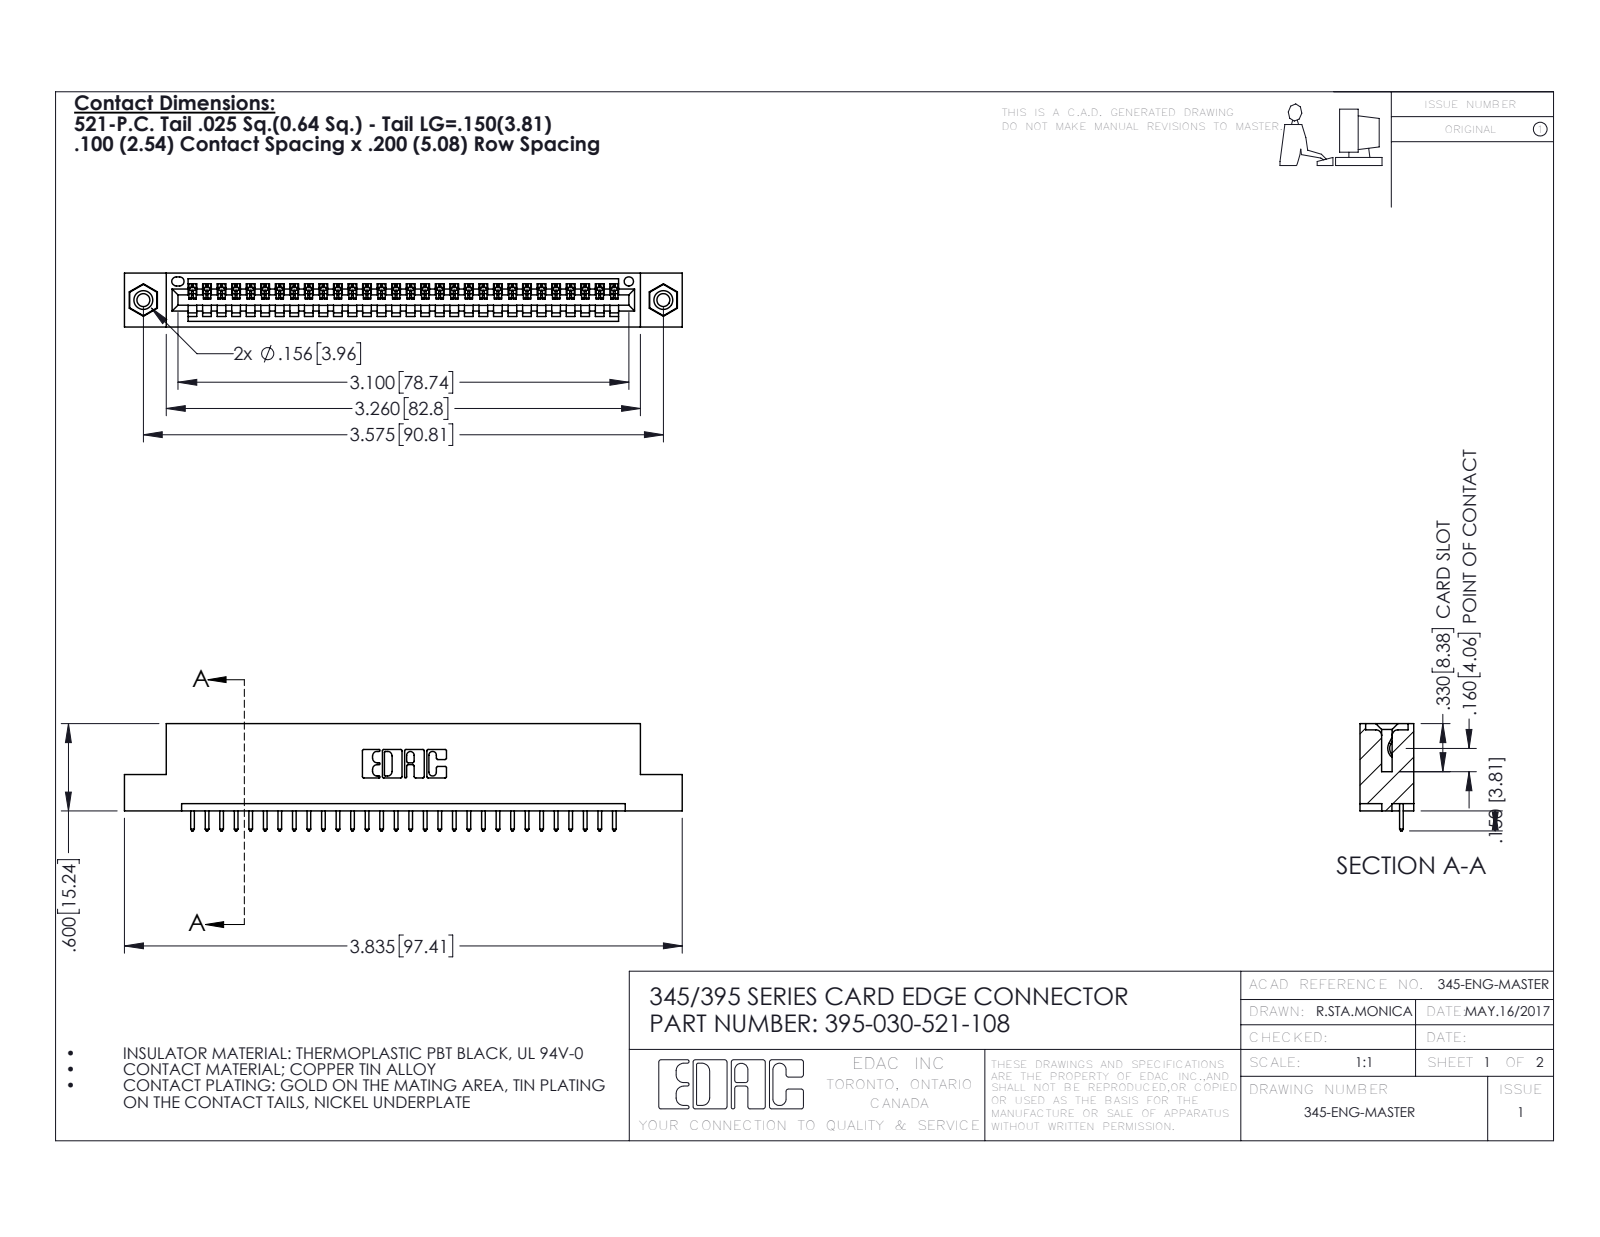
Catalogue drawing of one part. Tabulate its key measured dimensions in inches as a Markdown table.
| quantity | value |
| --- | --- |
| part name | 345-292-001_345-293-121; 345 Part_Flush Mounting Lugs - 0.156 Dia-TI; 395-030-521-108; 345-250-001_345-250-003-102 |
| STEP written by | SolidWorks 2016 (CONFIG_CONTROL_DESIGN) |
| units | inches |
| bodies | 33 solids, 1926 faces (1312 planar, 598 cylindrical, 16 other) |
| overall size | 3.835 × 0.737 × 0.37 |
| volume | 0.553 in³ |
| surface area | 17.93 in² |
| round holes (diameter × count) | 0.089 × 2, 0.125 × 2, 0.156 × 2, 0.064 × 1 |
| round bosses / shafts (diameter × count) | 0.155 × 2 |
| partial cylindrical surfaces (radius × count) | 0.006 × 60, 0.01 × 60, 0.01 × 22, 0.007 × 6, 0.031 × 6, 0.026 × 3, 0.031 × 2, 0.04 × 2 |
| main face-to-face distances | 0.072, 0.298, 0.37, 0.2, 0.098, 0.272, 0.025, 0.225, 0.149, 0.072 |
| hole center spacings | 0.27, 3.34, 3.575 |
